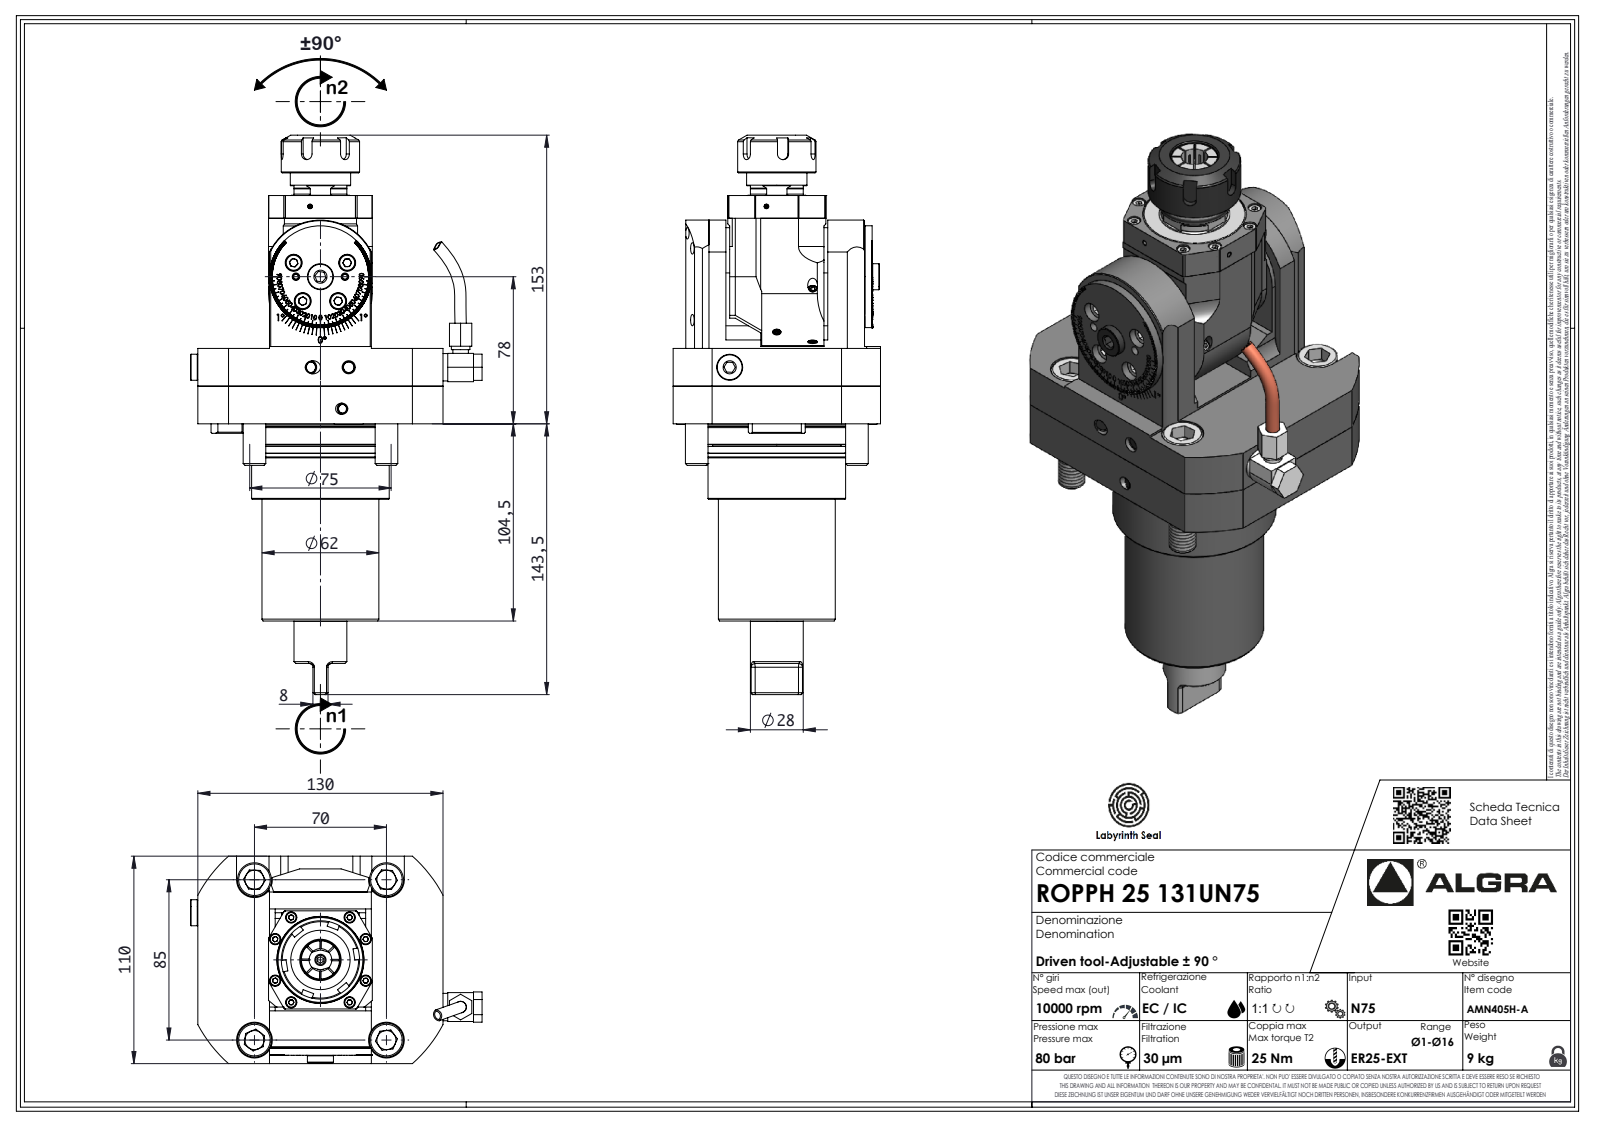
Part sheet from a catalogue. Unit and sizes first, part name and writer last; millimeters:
Units: millimetres
Overall size (bounding box): 296.53 × 150.7 × 110
Round holes (diameter × count): ⌀2.1 ×1, ⌀4 ×1
Round bosses / shafts (diameter × count): ⌀75 ×1, ⌀74.6 ×1, ⌀73 ×1, ⌀68 ×1, ⌀62 ×1, ⌀54 ×1, ⌀41.5 ×1, ⌀32 ×1
Partial cylindrical surfaces — rounded edges, fillets, slot ends (radius × count): R1 ×8, R4 ×8, R0.33 ×7, R0.52 ×7, R3.7 ×7, R2 ×6, R10 ×6, R3 ×5
Main face-to-face distances: 40, 1, 81, 80, 54.5, 38, 41, 92, 0.5, 37.5
Volume: 1 299 000 mm³ · Surface area: 114 956 mm²
Bodies: 1 solid, 639 faces (402 planar, 124 cylindrical, 113 other)
Part name (STEP PRODUCT): ROPPH25131UN75
STEP written by: SolidWorks 2023 (AUTOMOTIVE_DESIGN)
